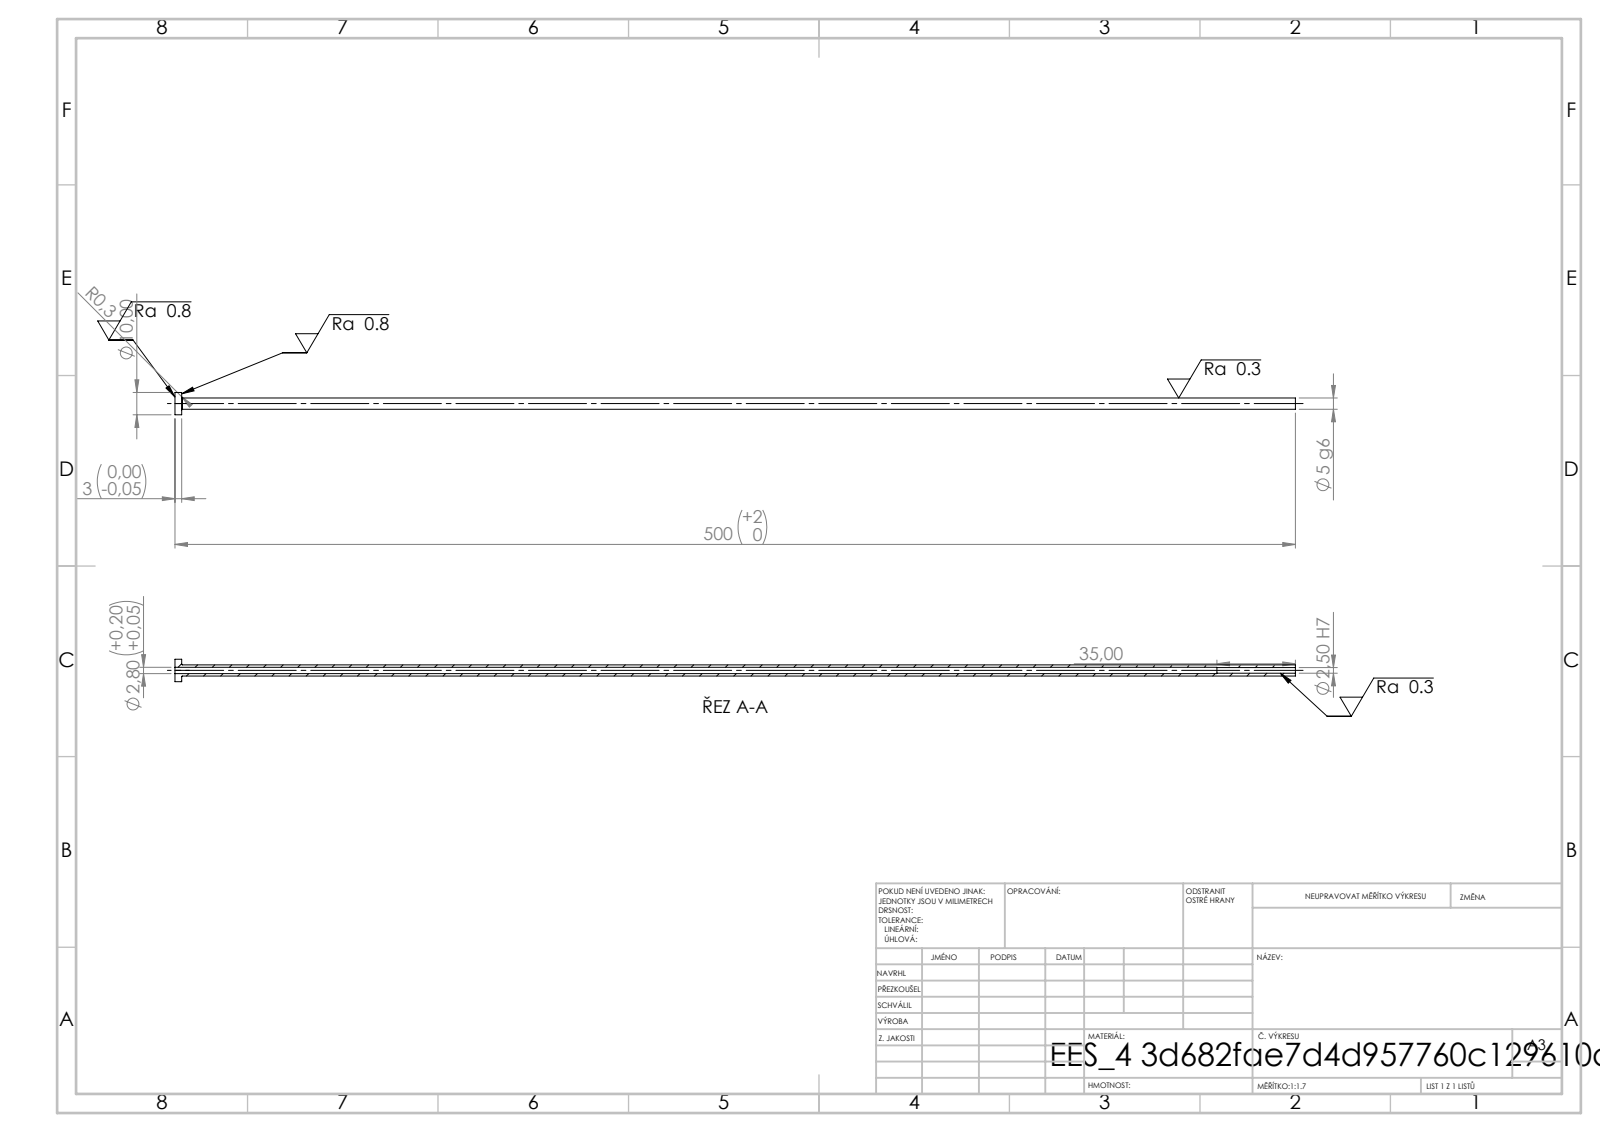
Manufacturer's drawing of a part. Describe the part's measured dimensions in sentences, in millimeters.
Its 3-D file was written by "SolidWorks 2019 (CONFIG_CONTROL_DESIGN)". It is 1 solid with 14 faces: 4 planar, 8 cylindrical and 2 other. Overall it measures 500 by 10 by 10 millimeters. Its volume is 6 959 cubic millimeters and its surface area 12 412 square millimeters. Round holes: 1 of diameter 2.5, 1 of diameter 2.8. Round bosses or shafts: 1 of diameter 10, 1 of diameter 5. The main face-to-face distances are 3, 500, 497, 465, 462, 35.
